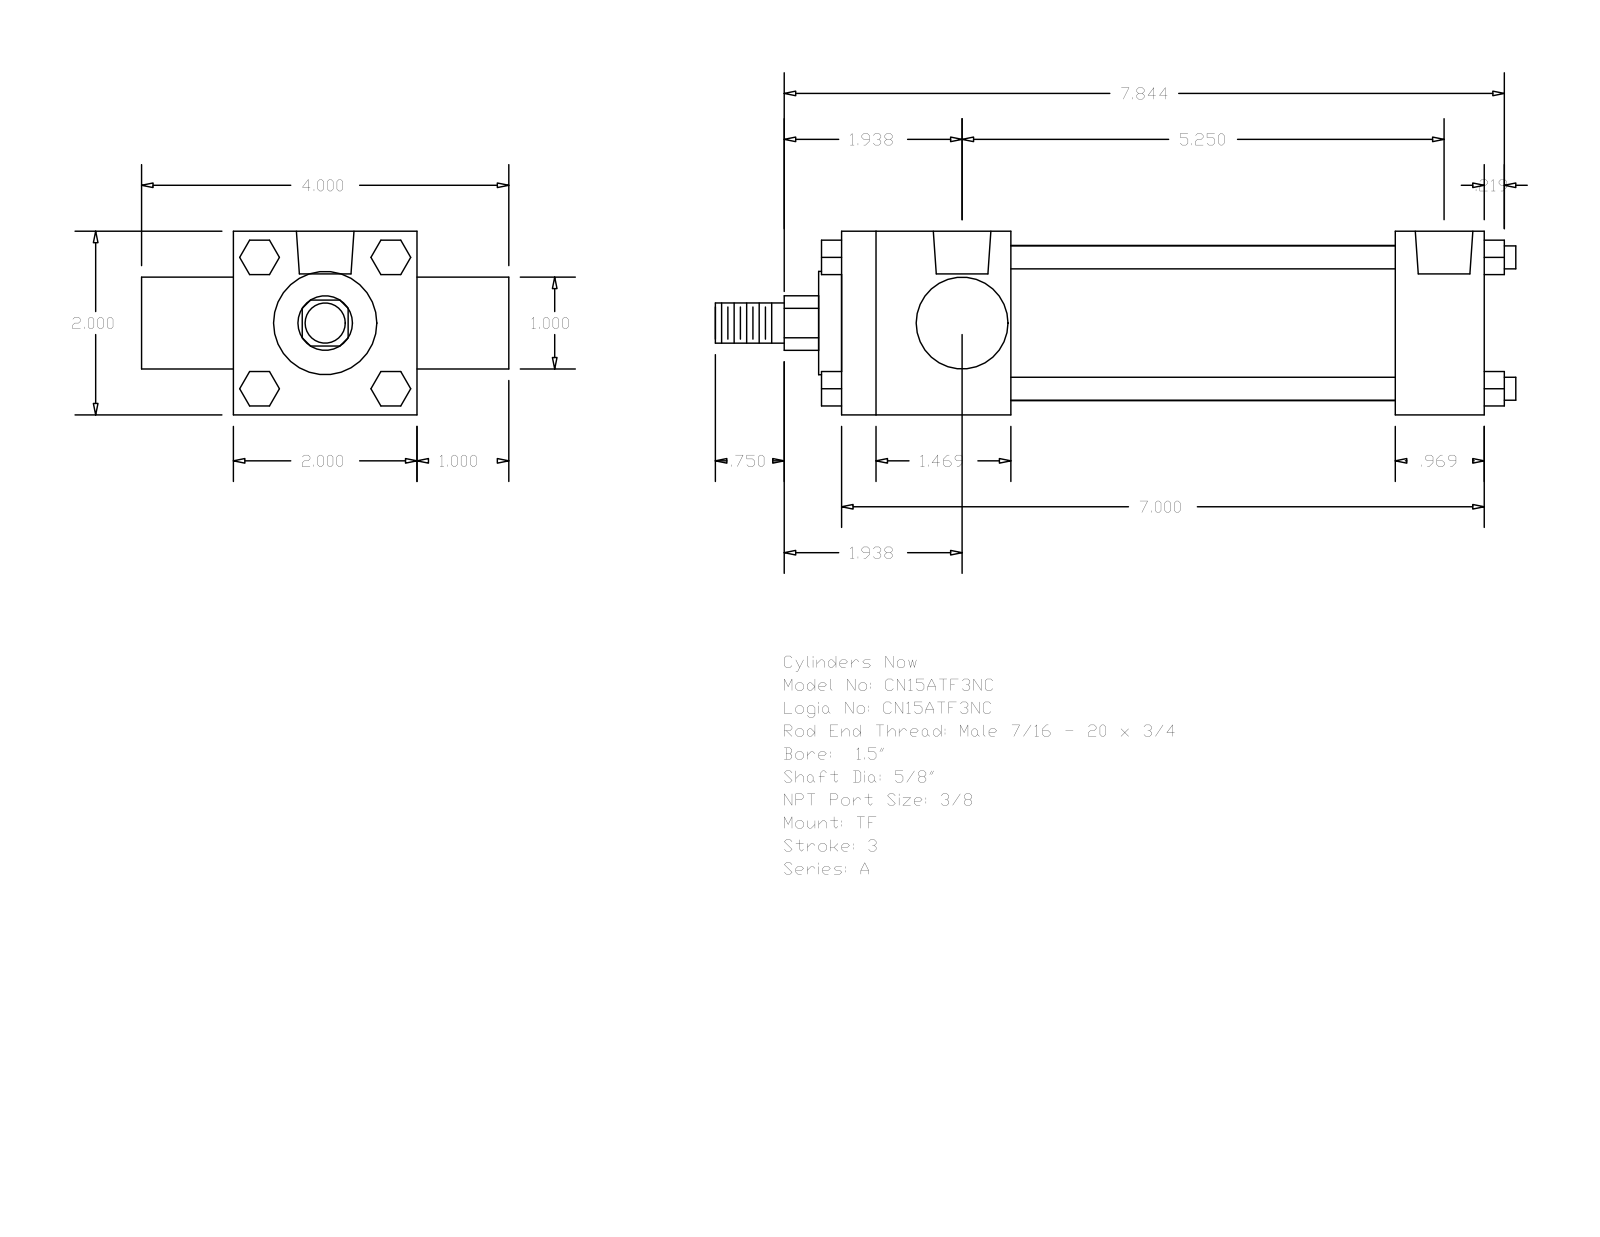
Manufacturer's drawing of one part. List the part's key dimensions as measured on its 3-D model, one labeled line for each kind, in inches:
Part name (STEP PRODUCT): A_TF__0150_0.625
STEP written by: GSSL Pune (CONFIG_CONTROL_DESIGN)
Units: inches
Bodies: 0 solids, 120 faces (92 planar, 28 cylindrical, 0 other)
Overall size (bounding box): 8.719 × 4 × 2
Round holes (diameter × count): ⌀0.219 ×3, ⌀0.627 ×2
Round bosses / shafts (diameter × count): ⌀0.25 ×4, ⌀1.69 ×1, ⌀1.125 ×1, ⌀1 ×1, ⌀0.625 ×1, ⌀0.437 ×1
Partial cylindrical surfaces — rounded edges, fillets, slot ends (radius × count): R0.297 ×1
Main face-to-face distances: 2, 7, 1, 3, 1.844, 6.031, 4.187, 5.156, 0.969, 4
Hole centre spacings: 0.156, 5.094, 4.937, 5.25
